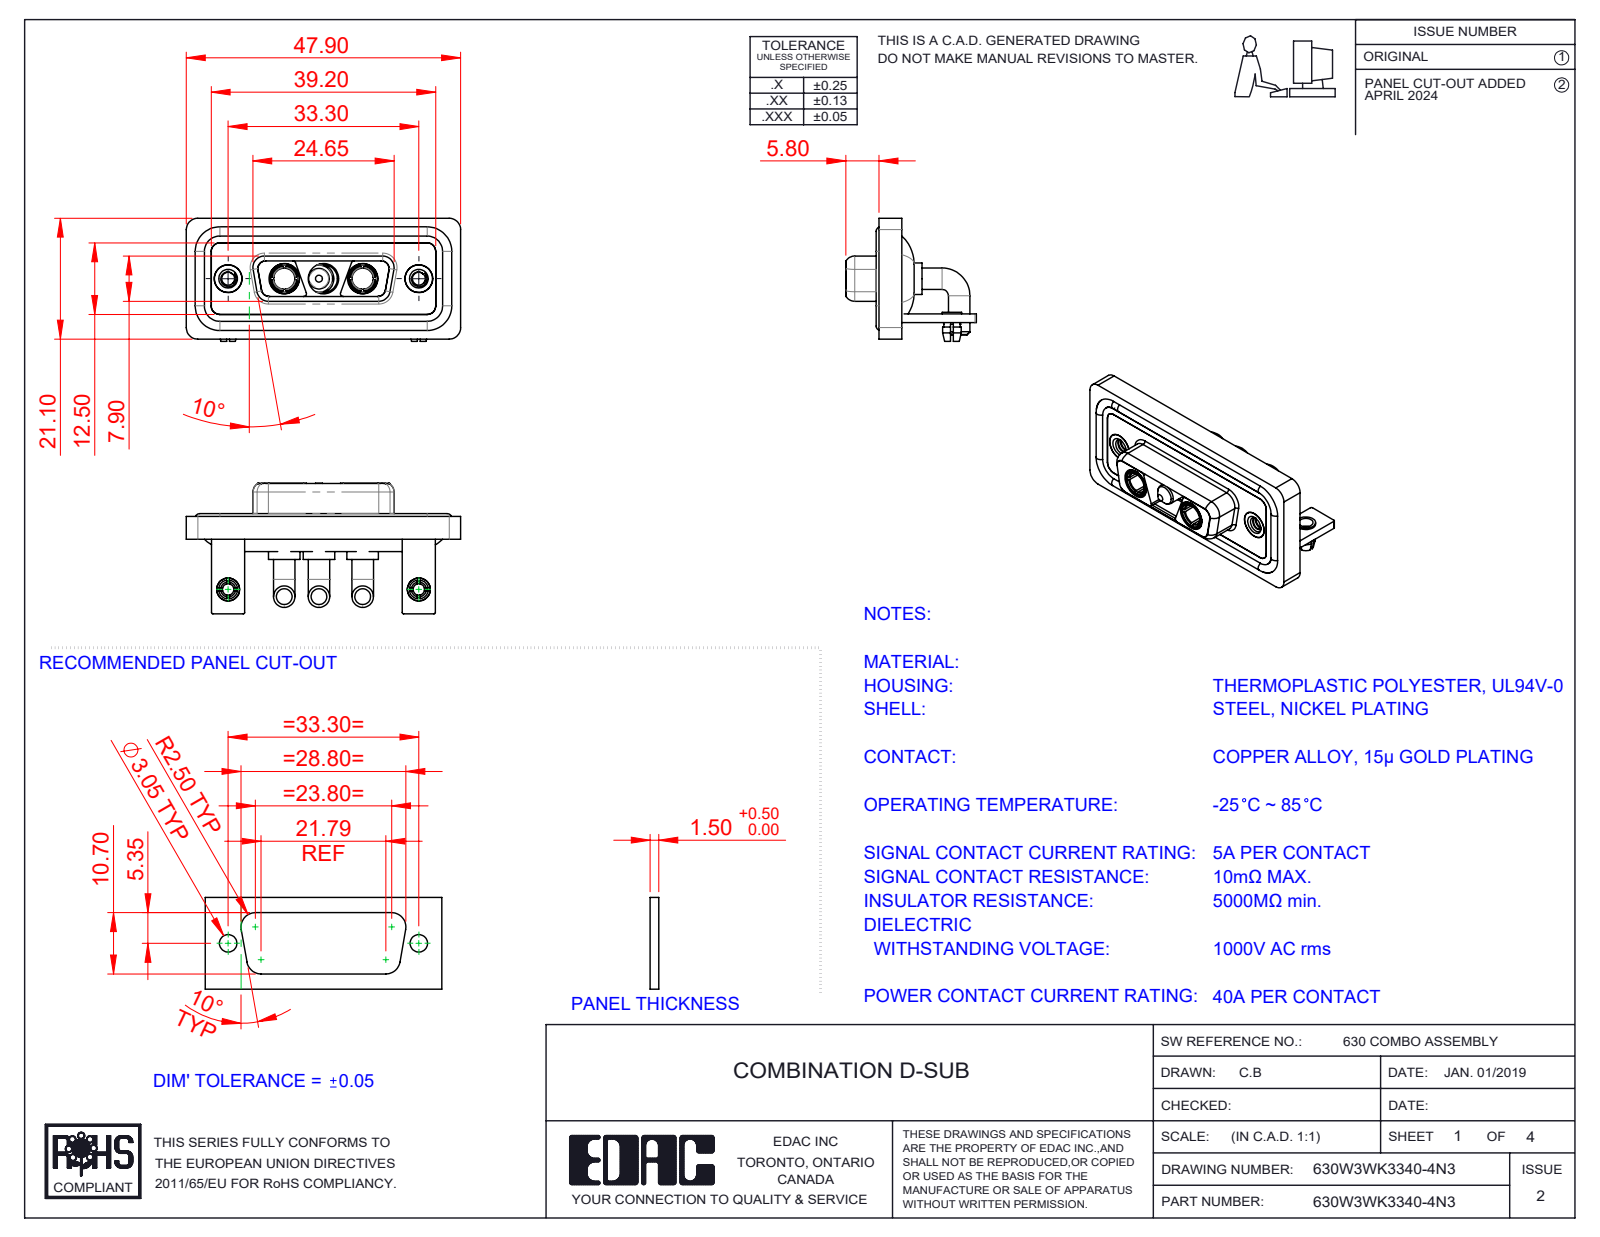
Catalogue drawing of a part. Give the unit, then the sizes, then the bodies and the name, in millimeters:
Units: millimetres
Overall size (bounding box): 47.9 × 22.8 × 21.5
Round holes (diameter × count): ⌀4.85 ×5, ⌀5.3 ×3, ⌀2 ×2, ⌀2.26 ×2, ⌀2.5 ×2, ⌀3.2 ×2, ⌀3.7 ×2, ⌀4 ×2, ⌀4.05 ×2, ⌀5 ×2
Round bosses / shafts (diameter × count): ⌀3.75 ×6, ⌀1.6 ×4, ⌀5.5 ×3, ⌀5.2 ×3, ⌀4.75 ×3, ⌀4.96 ×2, ⌀4.95 ×2, ⌀4.8 ×2
Partial cylindrical surfaces — rounded edges, fillets, slot ends (radius × count): R2 ×21, R1.5 ×18, R0.25 ×16, R1.35 ×12, R0.5 ×9, R1.6 ×8, R0.6 ×4, R0.65 ×4
Main face-to-face distances: 0.4, 2.9, 1.5, 3.7, 1.8, 1.1, 4.1, 1.6, 2.5, 1.4
Hole centre spacings: 6.85, 9.8, 16.65, 23.5, 33.3, 13.7
Volume: 6 653 mm³ · Surface area: 10 816 mm²
Bodies: 17 solids, 735 faces (246 planar, 320 cylindrical, 169 other)
Part name (STEP PRODUCT): 630Combo Threaded Rivet_2; 630Combo Stabilizer Bracket_50 Contacts; Power Socket_40A RA; 630Combo Waterproof Housing_15 Contacts (+6 more)
STEP written by: SolidWorks 2023 (CONFIG_CONTROL_DESIGN)
